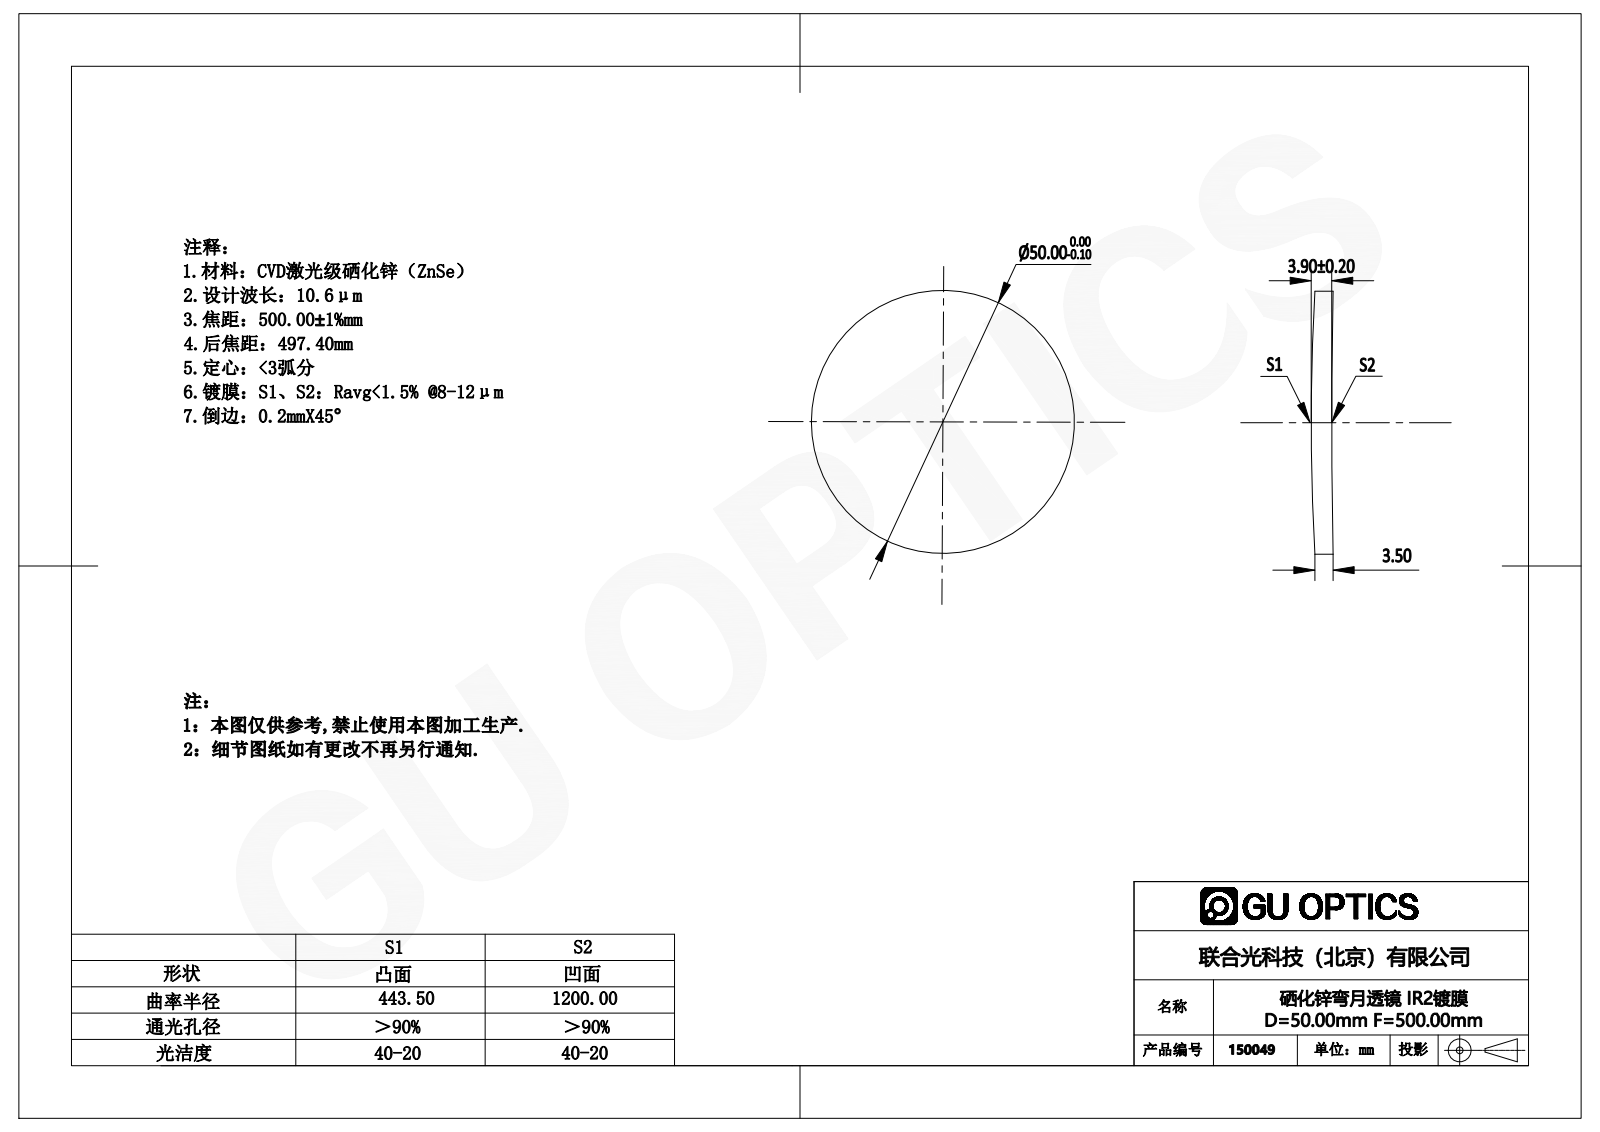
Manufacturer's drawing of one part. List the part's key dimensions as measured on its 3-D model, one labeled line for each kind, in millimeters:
Part name (STEP PRODUCT): 150024
STEP written by: SolidWorks 2016 (AUTOMOTIVE_DESIGN)
Units: millimetres
Bodies: 1 solid, 6 faces (0 planar, 2 cylindrical, 4 other)
Overall size (bounding box): 50 × 50 × 4.16
Volume: 7 221 mm³ · Surface area: 4 472 mm²
Round bosses / shafts (diameter × count): ⌀50 ×1
